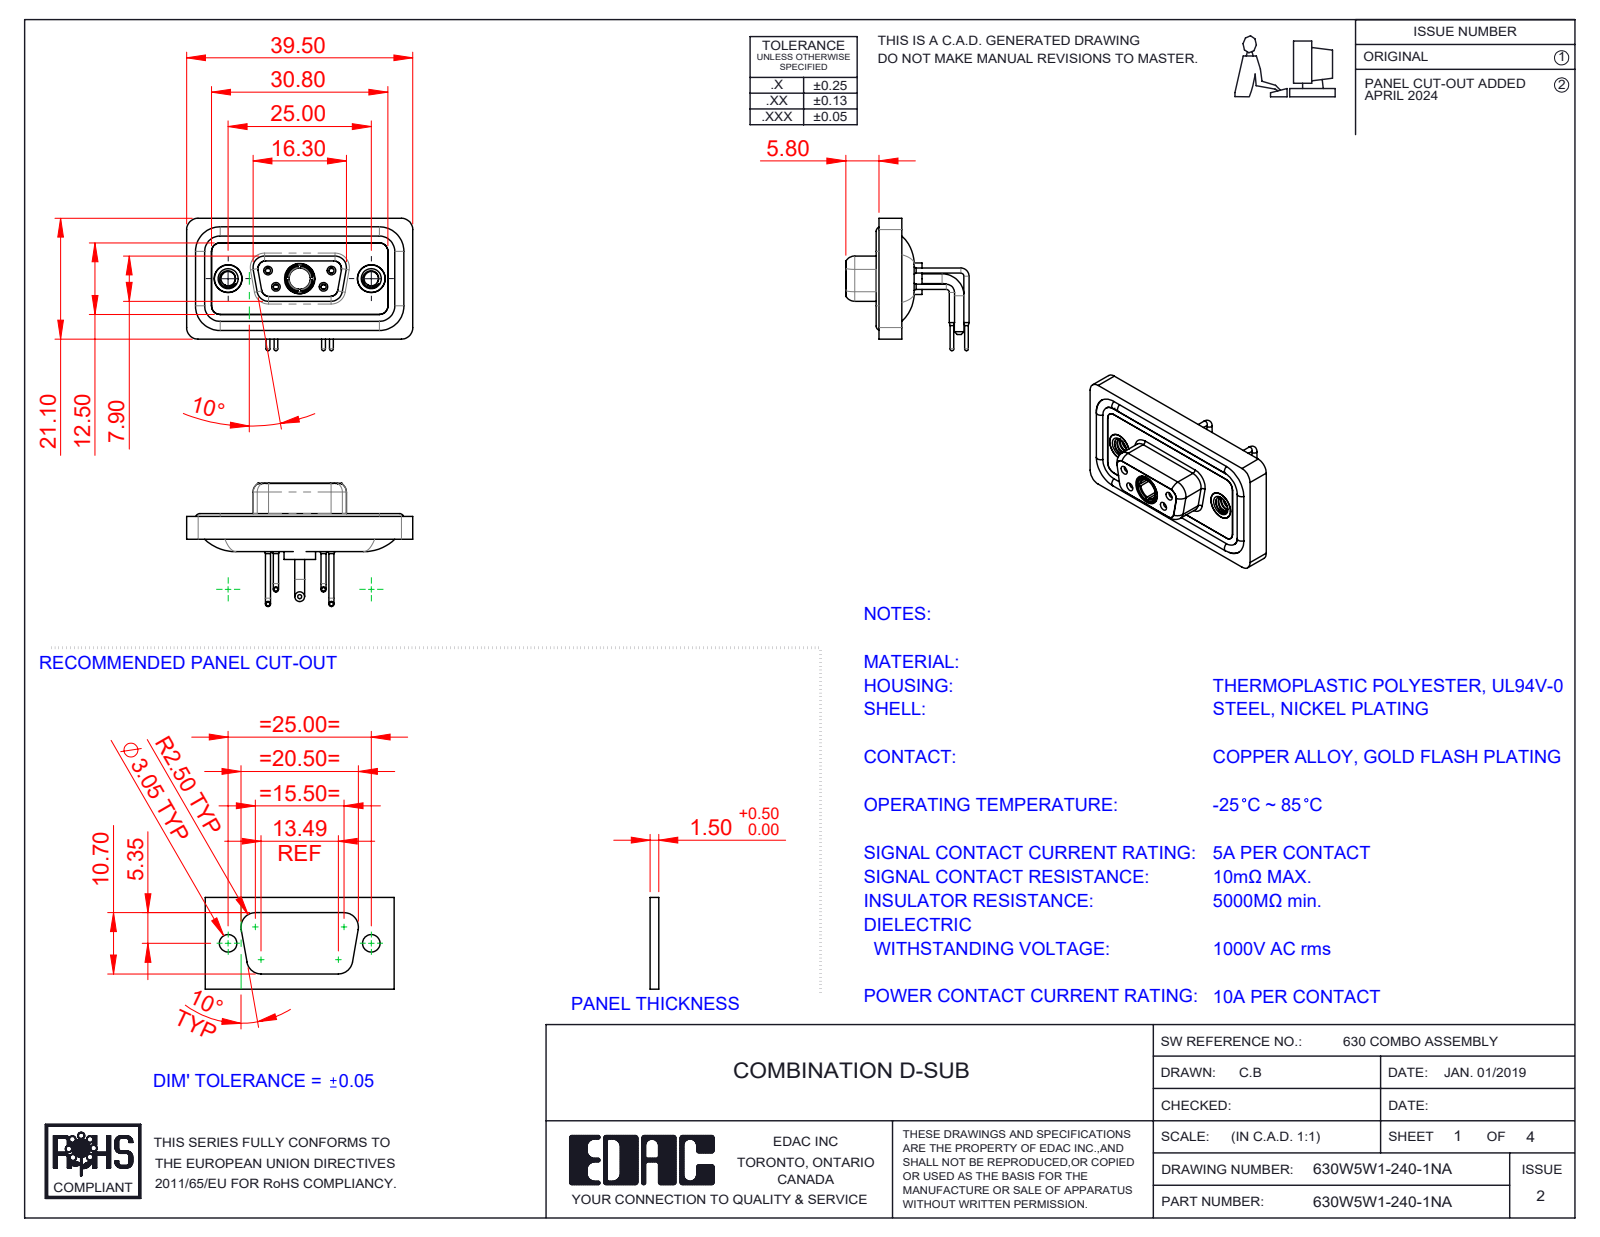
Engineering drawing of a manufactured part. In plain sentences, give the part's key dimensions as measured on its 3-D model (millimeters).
The part is named "630Combo Housing_5W1; 630Combo Contact Row 1_50 Contacts; 630Combo Waterproof Housing_09 Contacts; 630Combo Contact Row 2_50 Contacts (+5 more)". Its 3-D file was written by "SolidWorks 2023 (CONFIG_CONTROL_DESIGN)". It is 13 solids with 670 faces: 194 planar, 303 cylindrical and 173 other. Overall it measures 39.5 by 23.12 by 21.53 millimeters. Its volume is 4 764 cubic millimeters and its surface area 7 796 square millimeters. Round holes: 4 of diameter 0.9, 4 of diameter 1.1, 4 of diameter 1.5, 4 of diameter 2, 3 of diameter 4.85, 2 of diameter 1.6, 2 of diameter 1.7, 2 of diameter 2.5, 2 of diameter 4, 2 of diameter 4.05, 2 of diameter 5, 1 of diameter 3.7. Round bosses or shafts: 6 of diameter 1.6, 4 of diameter 0.9, 4 of diameter 0.65, 2 of diameter 4.95, 2 of diameter 4.8, 2 of diameter 1.7, 1 of diameter 5.5, 1 of diameter 5.2. Partial cylindrical surfaces (rounded edges, fillets, slot ends): 18 of radius 1.5, 18 of radius 2, 8 of radius 1.35, 8 of radius 1.6, 4 of radius 0.25, 4 of radius 0.5, 4 of radius 0.6, 4 of radius 0.65. The main face-to-face distances are 0.4, 1.8, 1.1, 2.9, 2.5, 1.6, 3.1, 1.5, 2.1, 0.5. The hole center spacings are 3.16, 5.72, 7.1, 12.5, 18.1, 4.39, 4.4, 8.31.
